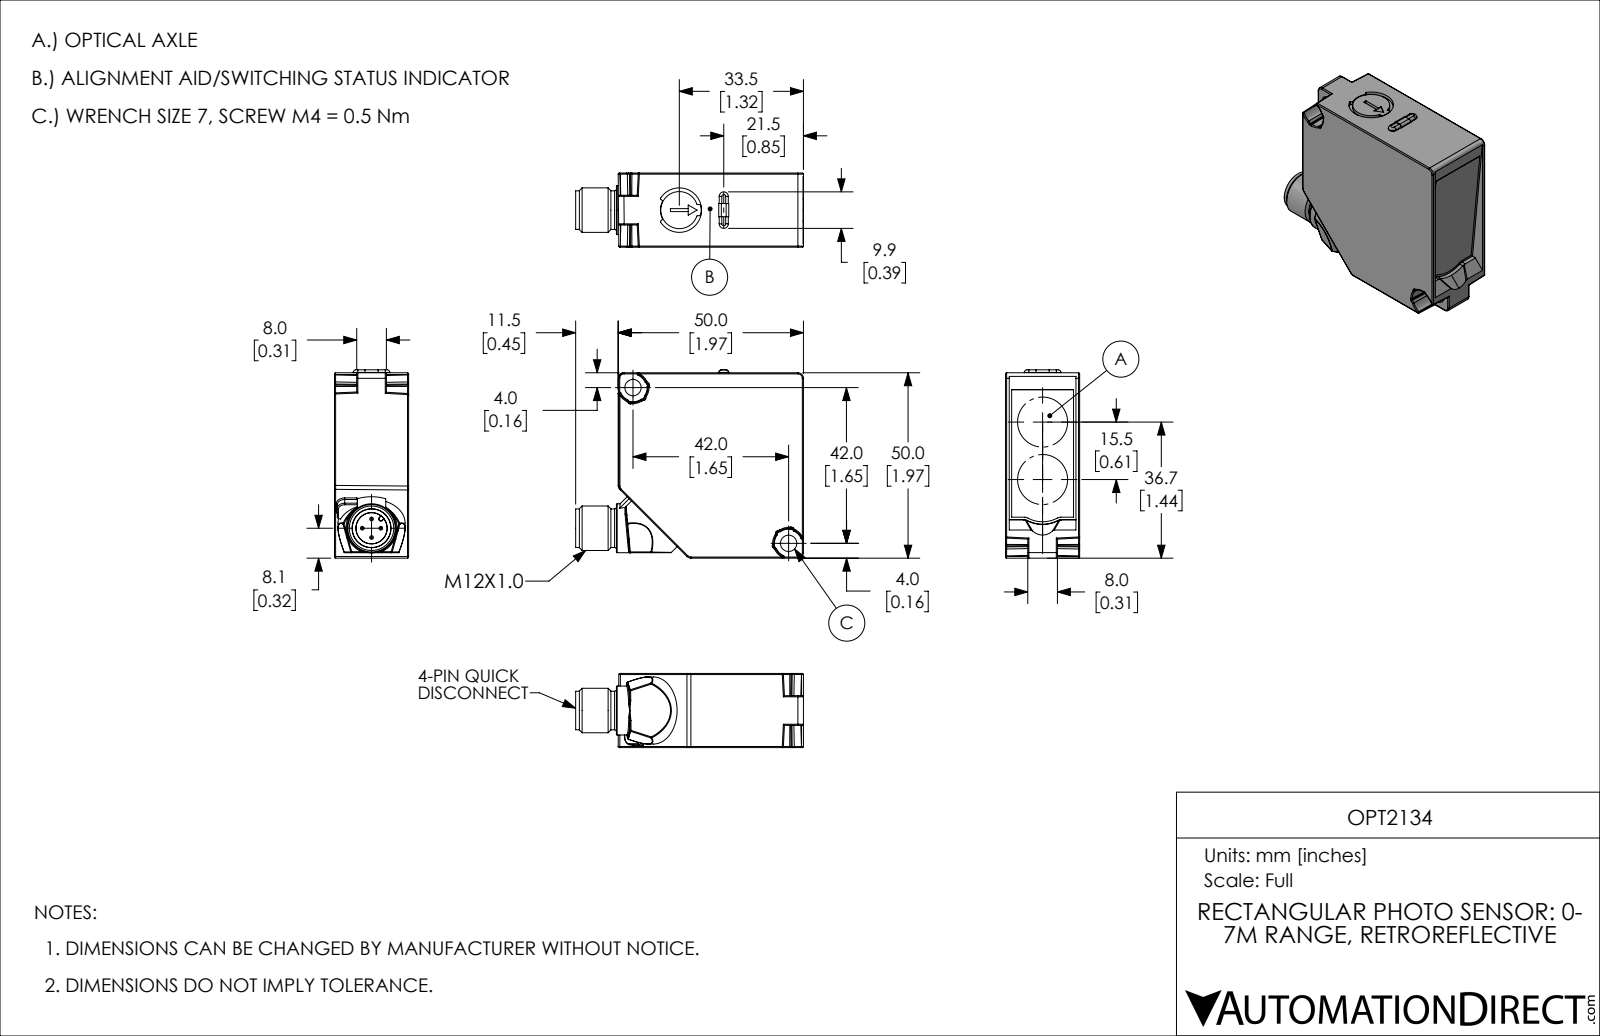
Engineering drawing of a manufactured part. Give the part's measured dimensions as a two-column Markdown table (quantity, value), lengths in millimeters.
| quantity | value |
| --- | --- |
| part name | OPT2134 |
| STEP written by | SolidWorks 2019 (AUTOMOTIVE_DESIGN) |
| units | millimeters |
| bodies | 2 solids, 342 faces (110 planar, 119 cylindrical, 113 other) |
| overall size | 61.5 × 50.8 × 20 |
| volume | 46 150 mm³ |
| surface area | 10 650 mm² |
| round holes (diameter × count) | 4.4 × 2, 12 × 1, 18.1 × 1 |
| round bosses / shafts (diameter × count) | 1 × 4, 13.2 × 1, 12 × 1, 10.4 × 1, 10 × 1 |
| partial cylindrical surfaces (radius × count) | 0.3 × 63, 0.2 × 8, 1.5 × 5, 2 × 5, 0.7 × 4, 1.2 × 2, 5.1 × 1, 5.9 × 1 |
| main face-to-face distances | 20, 50, 1, 19, 6, 14, 5, 13, 1.5, 48.5 |
| hole center spacings | 59.4 |
